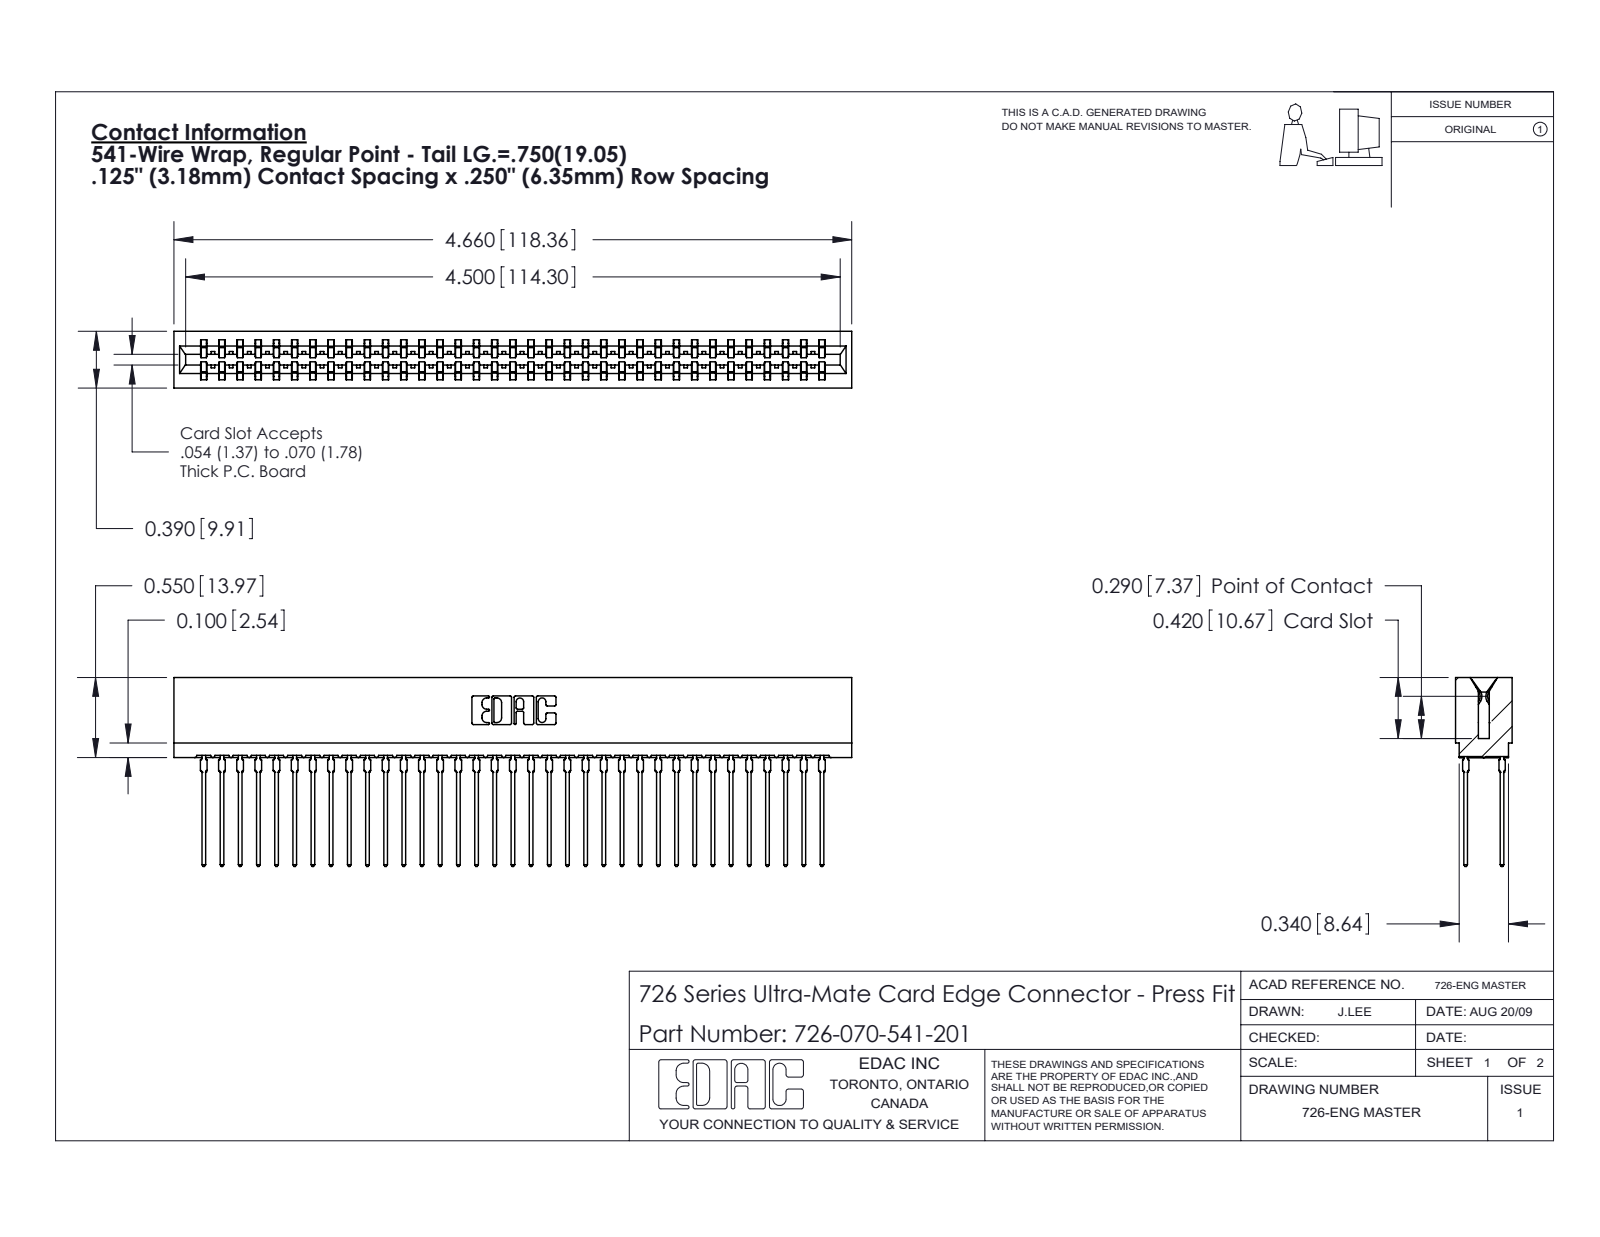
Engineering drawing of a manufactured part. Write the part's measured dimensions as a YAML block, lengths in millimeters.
part_name: "726-070-541-201; 746-292-001_541; 726 Part_.515 Slot Depth - 01"
step_written_by: "SolidWorks 2020 (CONFIG_CONTROL_DESIGN)"
units: millimeters
bodies: {solids: 71, faces: 6362, planar: 3275, cylindrical: 1267, other: 1820}
overall_size: [118.4, 33, 9.9]
volume: 11300
surface_area: 20520
partial_cylinders:
  - {radius: 0.5, count: 140}
  - {radius: 0.4, count: 36}
  - {radius: 0.3, count: 22}
  - {radius: 0.1, count: 8}
  - {radius: 0.3, count: 8}
  - {radius: 0.2, count: 6}
  - {radius: 0.8, count: 6}
  - {radius: 0.7, count: 3}
face_to_face_distances: [1.4, 8.5, 6.4, 0.6, 7.8, 2.1, 9.9, 7, 12.7, 5.7]
